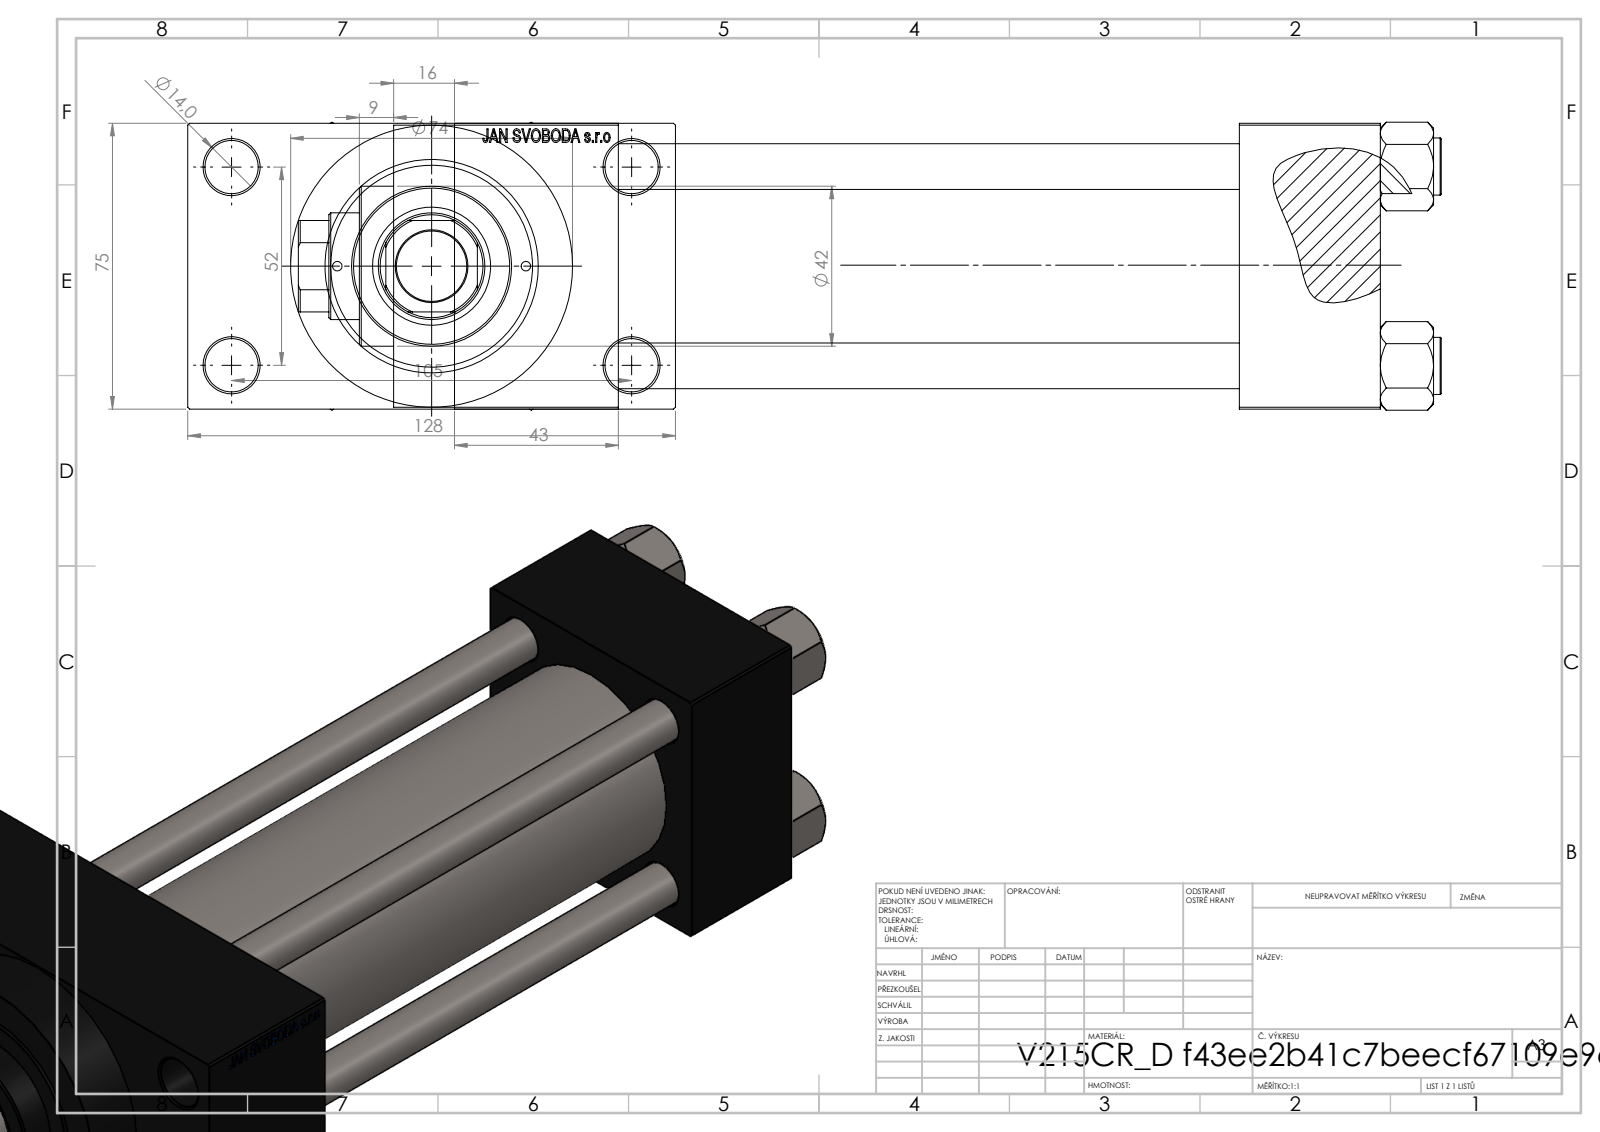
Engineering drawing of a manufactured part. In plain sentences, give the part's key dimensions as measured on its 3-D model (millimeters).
The part is named "V215CR_D_TYCINKA; V215CR_VCP_D; V215_VC_A; V215CR_D_Body (+1 more)". Its 3-D file was written by "SolidWorks 2019 (CONFIG_CONTROL_DESIGN)". It is 11 solids with 1111 faces: 499 planar, 92 cylindrical and 520 other. Overall it measures 300 by 128 by 75.54 millimeters. Its volume is 970 573 cubic millimeters and its surface area 230 579 square millimeters. Round holes: 4 of diameter 12, 4 of diameter 14, 2 of diameter 2.5, 2 of diameter 7, 2 of diameter 20.96, 2 of diameter 30, 1 of diameter 18.5, 1 of diameter 28, 1 of diameter 31, 1 of diameter 41, 1 of diameter 50, 1 of diameter 53. Round bosses or shafts: 4 of diameter 15, 1 of diameter 74, 1 of diameter 56, 1 of diameter 42. Partial cylindrical surfaces (rounded edges, fillets, slot ends): 1 of radius 13.5. The main face-to-face distances are 75, 163, 37, 200, 26.5, 243, 206, 43, 101.5, 16. The hole center spacings are 26.19, 26.35, 36.98, 38.03, 52.3, 57.22, 58.43, 58.59.
